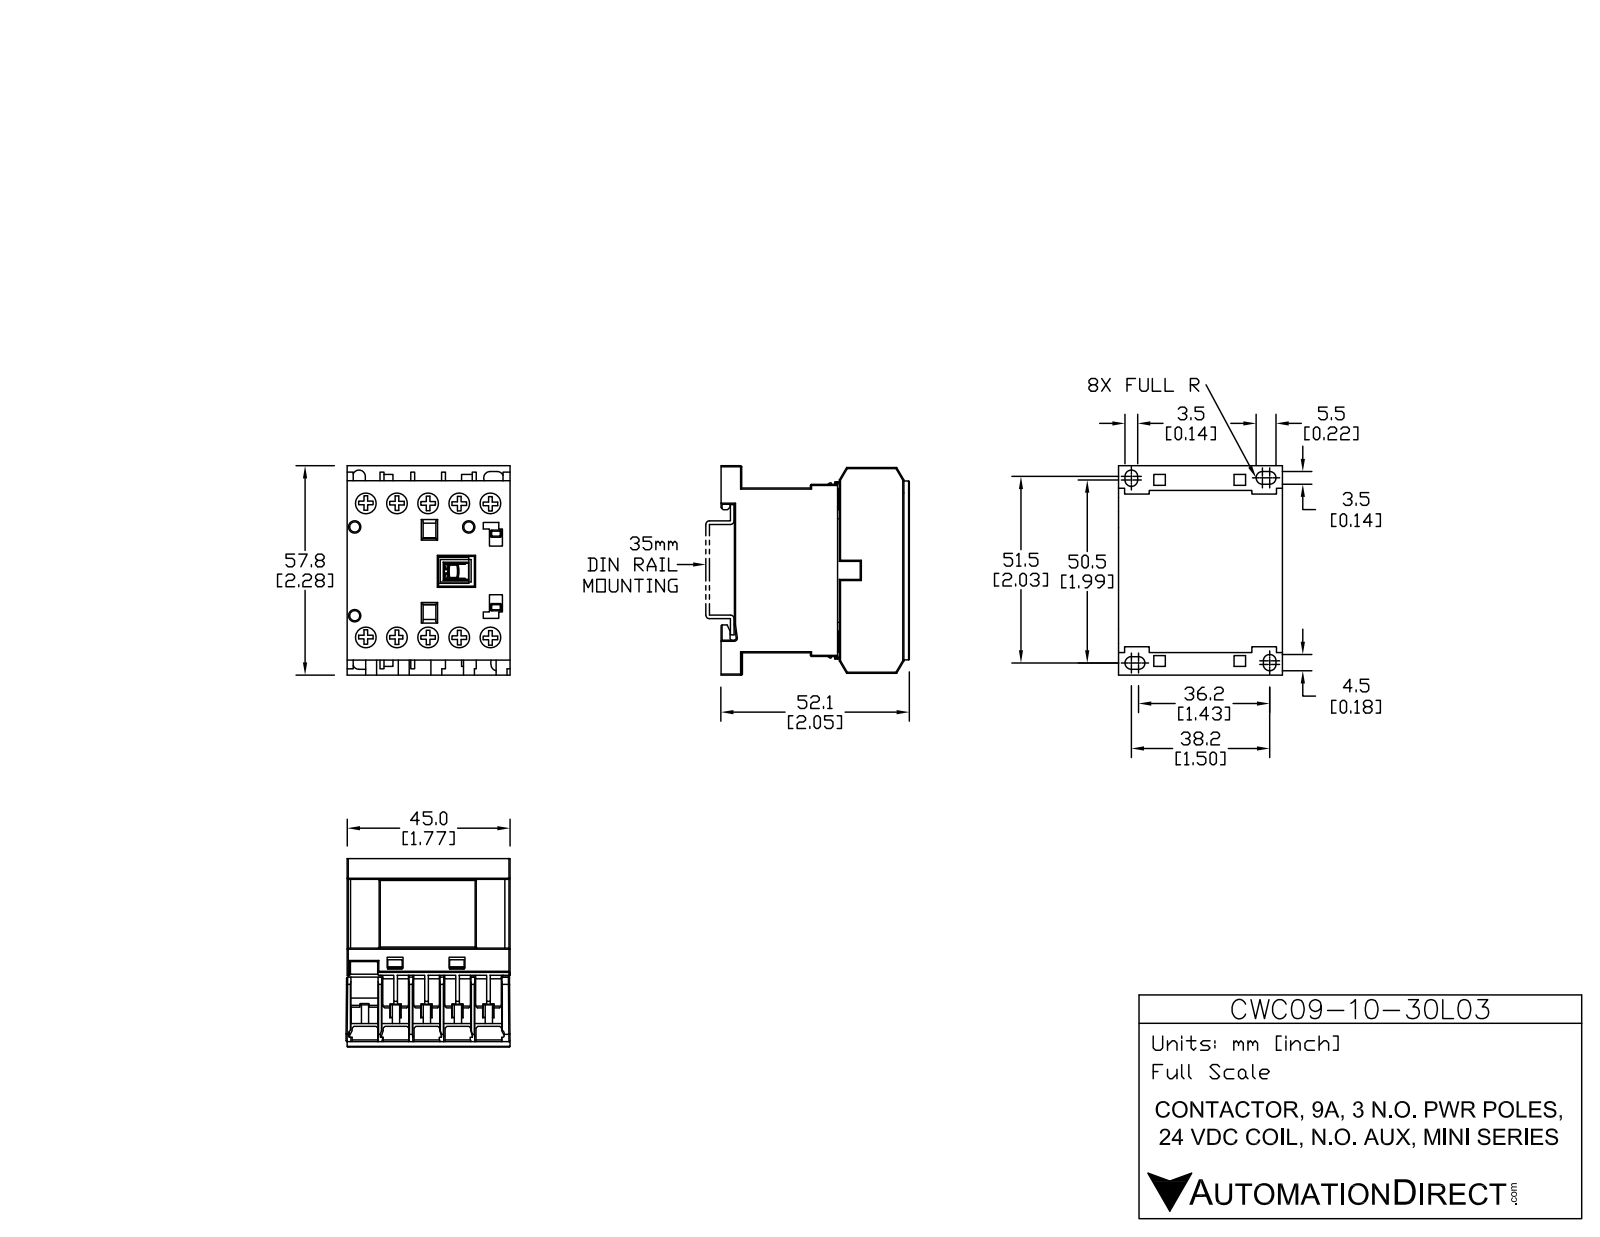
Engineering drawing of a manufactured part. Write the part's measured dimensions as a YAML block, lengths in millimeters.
part_name: "CWC09-10-30L03"
step_written_by: "SolidWorks 2013 (AUTOMOTIVE_DESIGN)"
units: millimeters
bodies: {solids: 15, faces: 535, planar: 445, cylindrical: 90, other: 0}
overall_size: [58.04, 52.12, 45.75]
volume: 97133
surface_area: 30437
round_holes:
  - {diameter: 6.2, count: 10}
  - {diameter: 2.8, count: 3}
round_bosses_or_shafts:
  - {diameter: 5.9, count: 10}
partial_cylinders:
  - {radius: 0.3, count: 20}
  - {radius: 1.72, count: 6}
  - {radius: 1.73, count: 2}
  - {radius: 0.32, count: 1}
  - {radius: 0.42, count: 1}
  - {radius: 0.55, count: 1}
face_to_face_distances: [8.25, 45.5, 1.25, 16.5, 9.5, 5.5, 17.75, 5.13, 10.63, 7]
hole_center_spacings: [8.55, 37.94, 17.1, 40.72, 36.96, 25.65, 44.99, 6.91]
